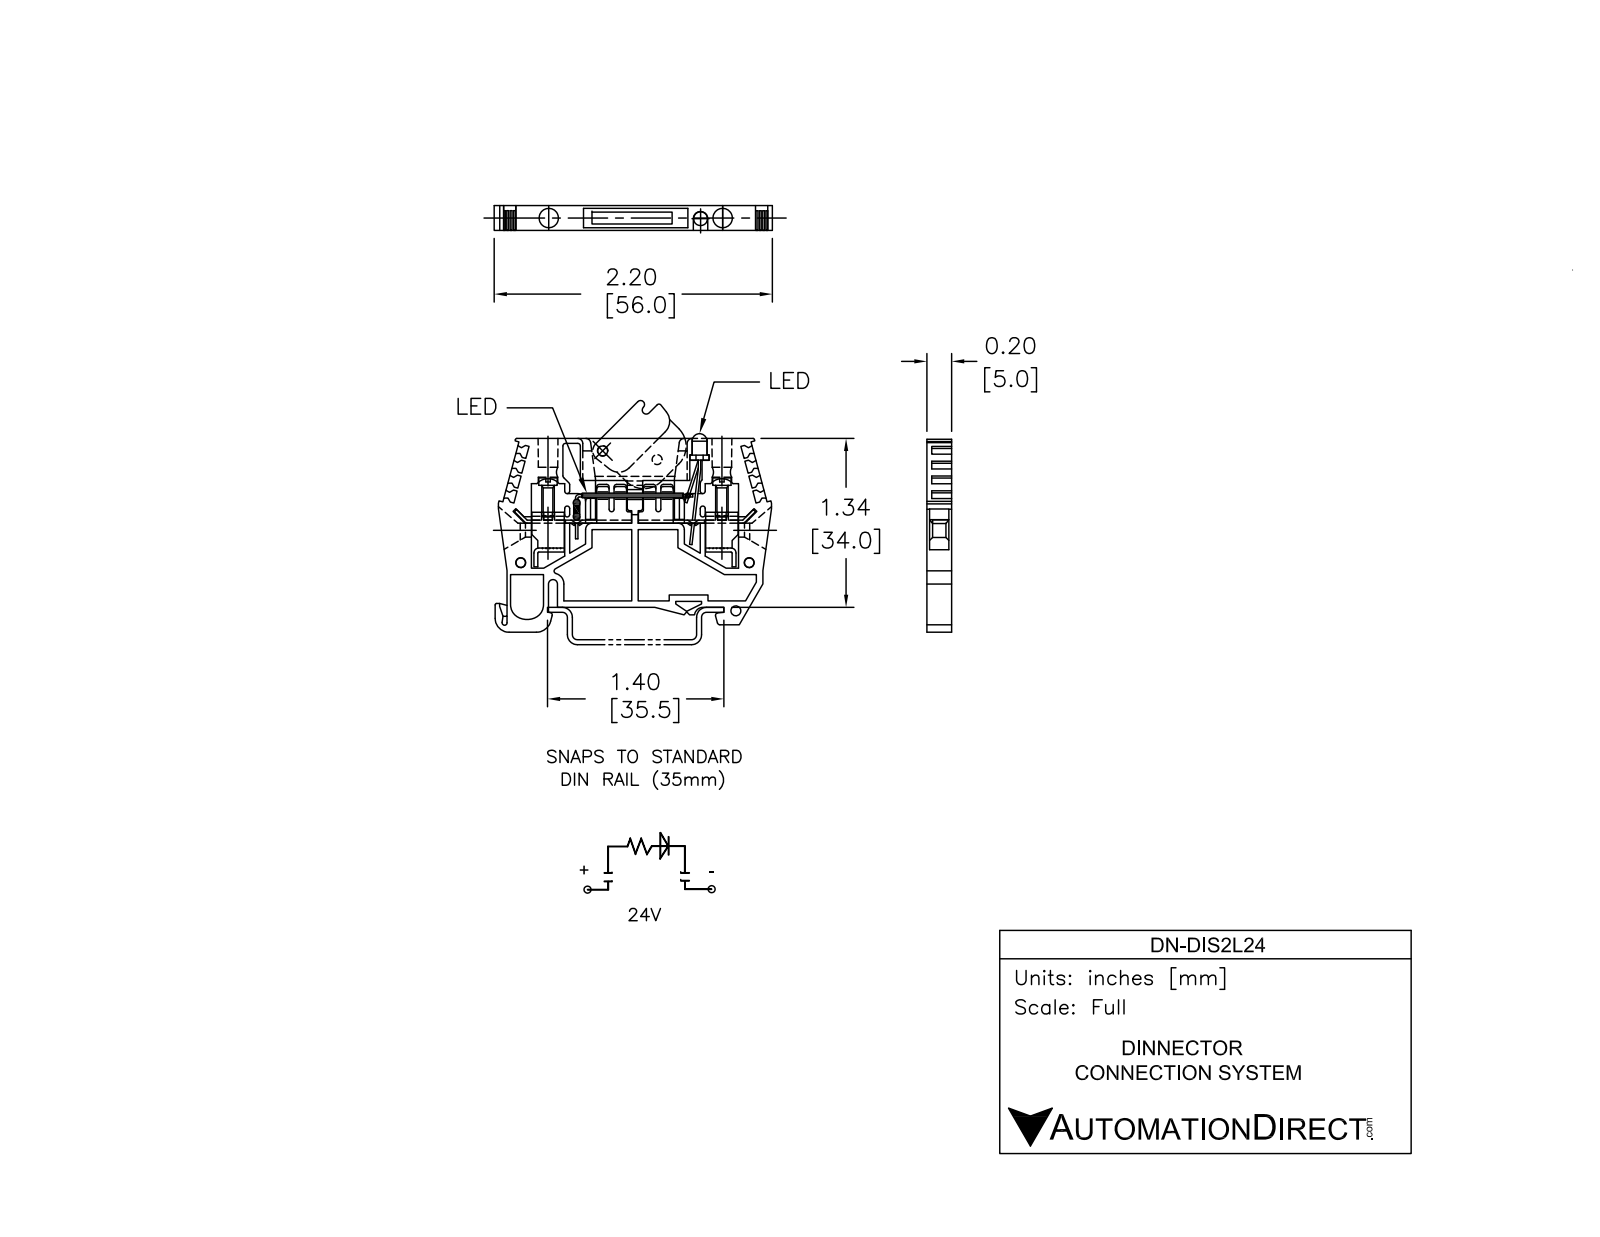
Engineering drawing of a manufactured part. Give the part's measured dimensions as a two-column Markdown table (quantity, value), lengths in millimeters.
| quantity | value |
| --- | --- |
| part name | 4358005_DN-D1S2L24; 4258000_DN-QFE2_1; 435K0001; 20621_1 |
| STEP written by | SolidWorks 2013 (AUTOMOTIVE_DESIGN) |
| units | millimeters |
| bodies | 3 solids, 403 faces (222 planar, 112 cylindrical, 69 other) |
| overall size | 55.65 × 39.6 × 5.95 |
| volume | 7 976 mm³ |
| surface area | 6 582 mm² |
| round holes (diameter × count) | 2 × 4, 4.1 × 2 |
| round bosses / shafts (diameter × count) | 0.3 × 10, 4 × 1, 3 × 1, 2 × 1 |
| partial cylindrical surfaces (radius × count) | 0.5 × 22, 3 × 7, 1 × 3, 0.8 × 2, 5 × 2, 0.9 × 1, 1.05 × 1, 1.7 × 1 |
| main face-to-face distances | 5, 2.2, 0.6, 34, 0.55, 4.45, 2.85, 2.25, 1, 3.9 |
| hole center spacings | 26.67, 10.07, 30.83, 35, 44.38, 46 |
